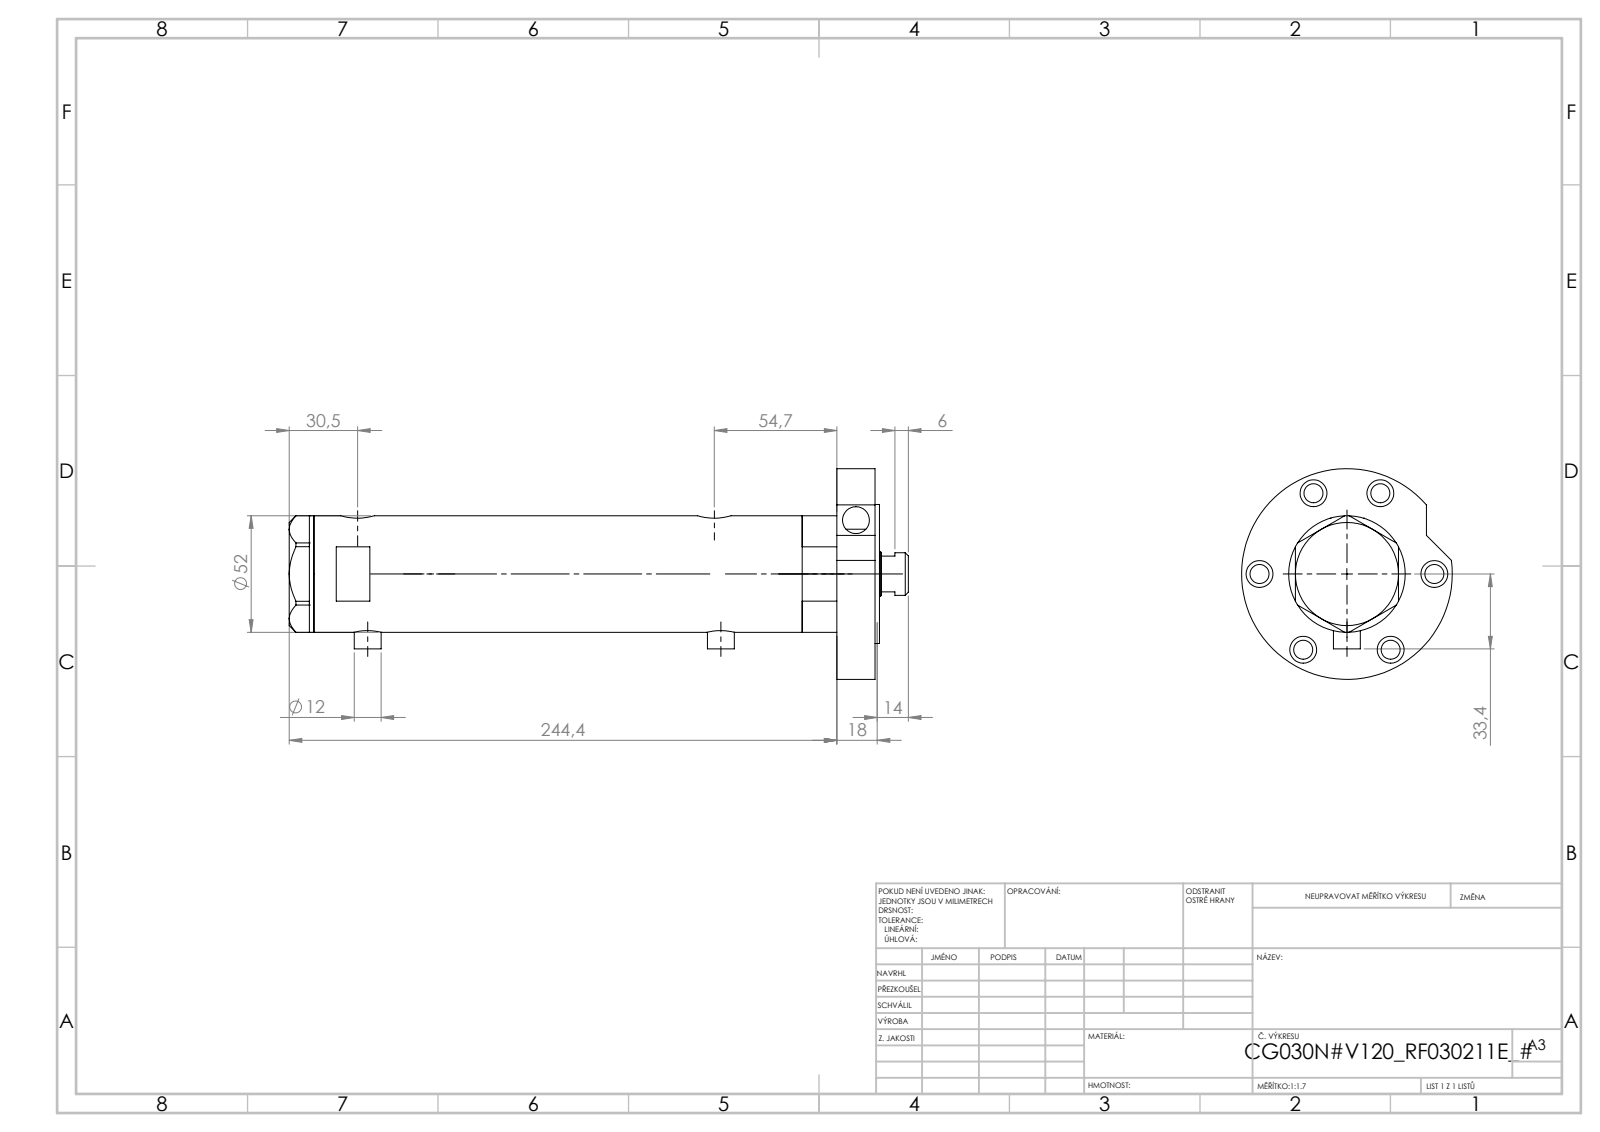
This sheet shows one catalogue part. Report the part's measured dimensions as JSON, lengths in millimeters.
{"part_name": "V270CG_BACK; V270CG_FRONT; V270CG_RF211E; V270CG_VC (+1 more)", "step_written_by": "SolidWorks 2019 (CONFIG_CONTROL_DESIGN)", "units": "millimeters", "bodies": {"solids": 5, "faces": 178, "planar": 76, "cylindrical": 82, "other": 20}, "overall_size": [276.3, 94, 94], "volume_mm3": 573866, "surface_area_mm2": 129935, "round_holes": [[12, 7], [8.5, 6], [9.73, 2], [12.5, 2], [15, 2], [6.5, 1], [20, 1], [21.5, 1], [30, 1], [33, 1], [40, 1], [44, 1]], "round_bosses_or_shafts": [[12, 2], [94, 1], [62, 1], [52, 1], [38, 1], [19, 1]], "face_to_face_distances": [17, 233.4, 250.4, 2, 252.4, 181.5, 51.9, 68.9, 70.9, 19], "hole_center_spacings": [39, 43.34, 64.85, 67.55, 69.95, 77.83, 2.9, 4.5]}
